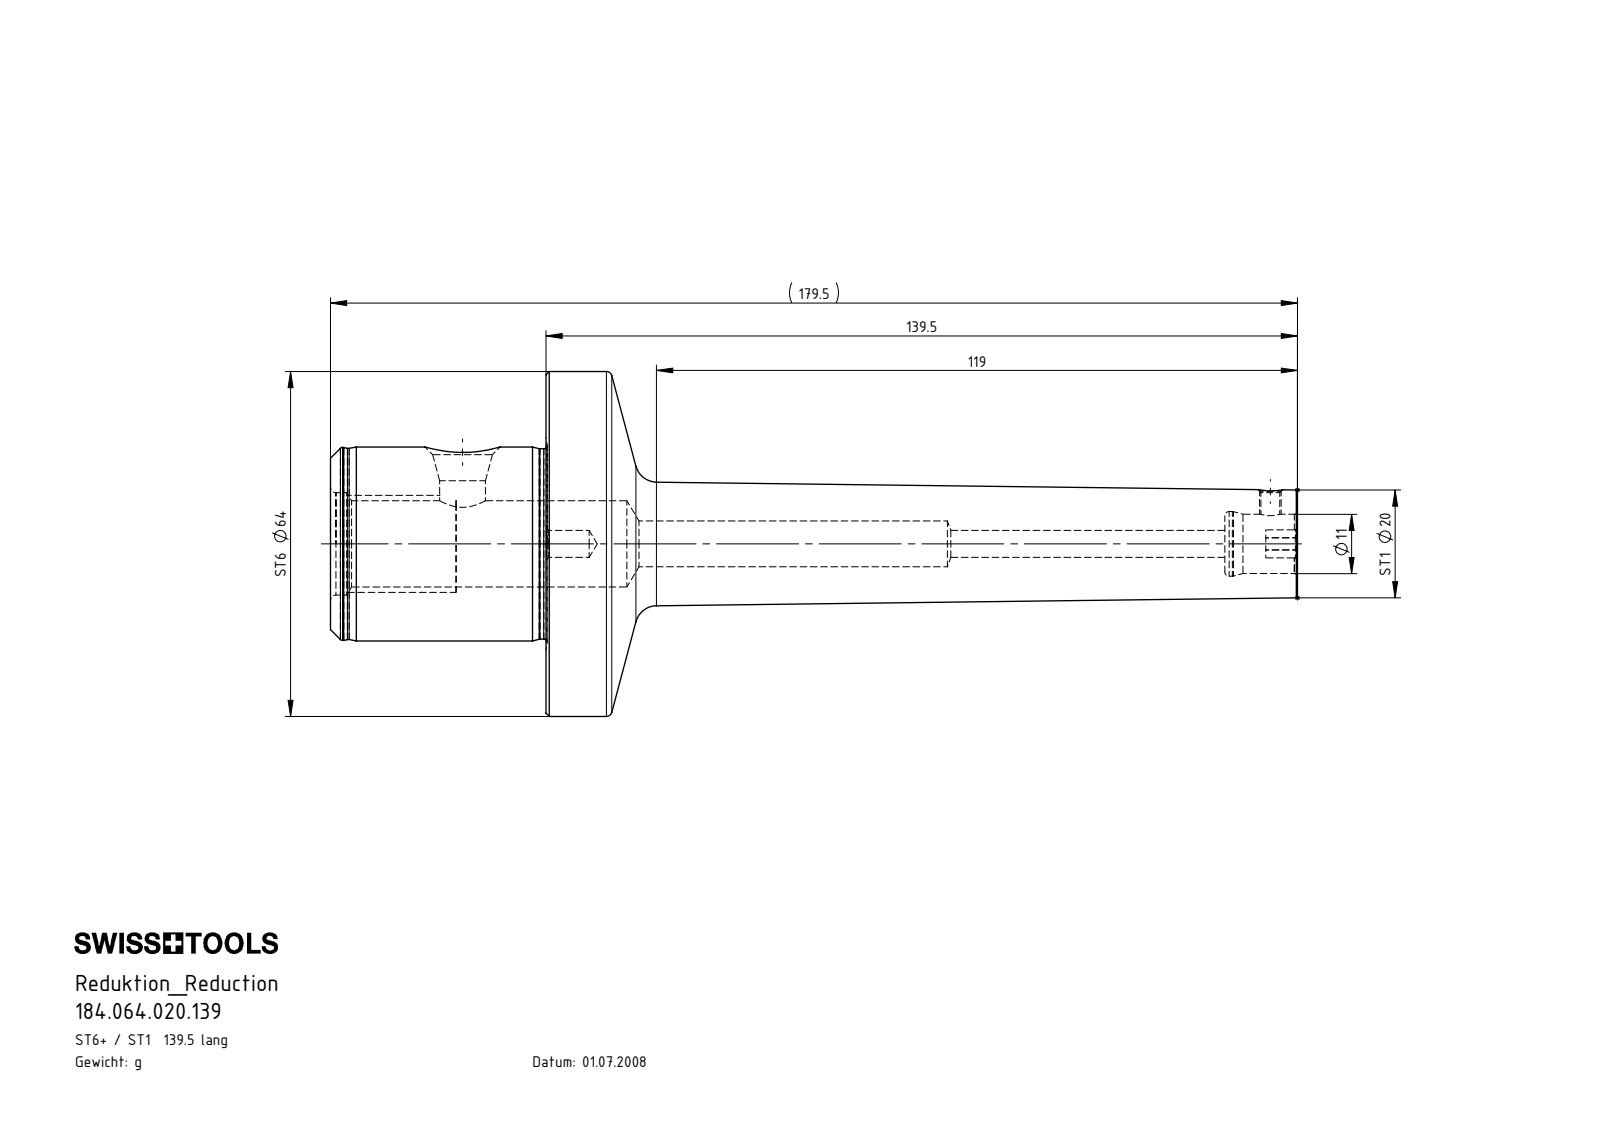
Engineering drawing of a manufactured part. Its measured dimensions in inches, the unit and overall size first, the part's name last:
Units: inches
Overall size (bounding box): 7.067 × 2.52 × 2.52
Round holes (diameter × count): ⌀0.197 ×2, ⌀0.138 ×1, ⌀0.165 ×1, ⌀0.335 ×1, ⌀0.433 ×1, ⌀0.472 ×1, ⌀0.63 ×1, ⌀0.748 ×1
Round bosses / shafts (diameter × count): ⌀2.52 ×1, ⌀1.417 ×1, ⌀1.409 ×1, ⌀1.39 ×1, ⌀0.157 ×1
Partial cylindrical surfaces — rounded edges, fillets, slot ends (radius × count): R0.02 ×4, R0.051 ×2, R0.215 ×2, R0.711 ×2
Main face-to-face distances: 1.575, 7.067, 5.492, 0.197, 1.378, 5.689, 6.535, 5.157, 4.961, 0.531
Hole centre spacings: 0.846, 1.693, 5.904
Volume: 7.166 in³ · Surface area: 42.27 in²
Bodies: 4 solids, 166 faces (26 planar, 47 cylindrical, 93 other)
Part name (STEP PRODUCT): ST6-ER2.001.012_A; ST6-ST1.K01.139; ST6-ST1.K01.139_A; ST1-ER1.001.005_A
STEP written by: SolidWorks 2015 (CONFIG_CONTROL_DESIGN)
